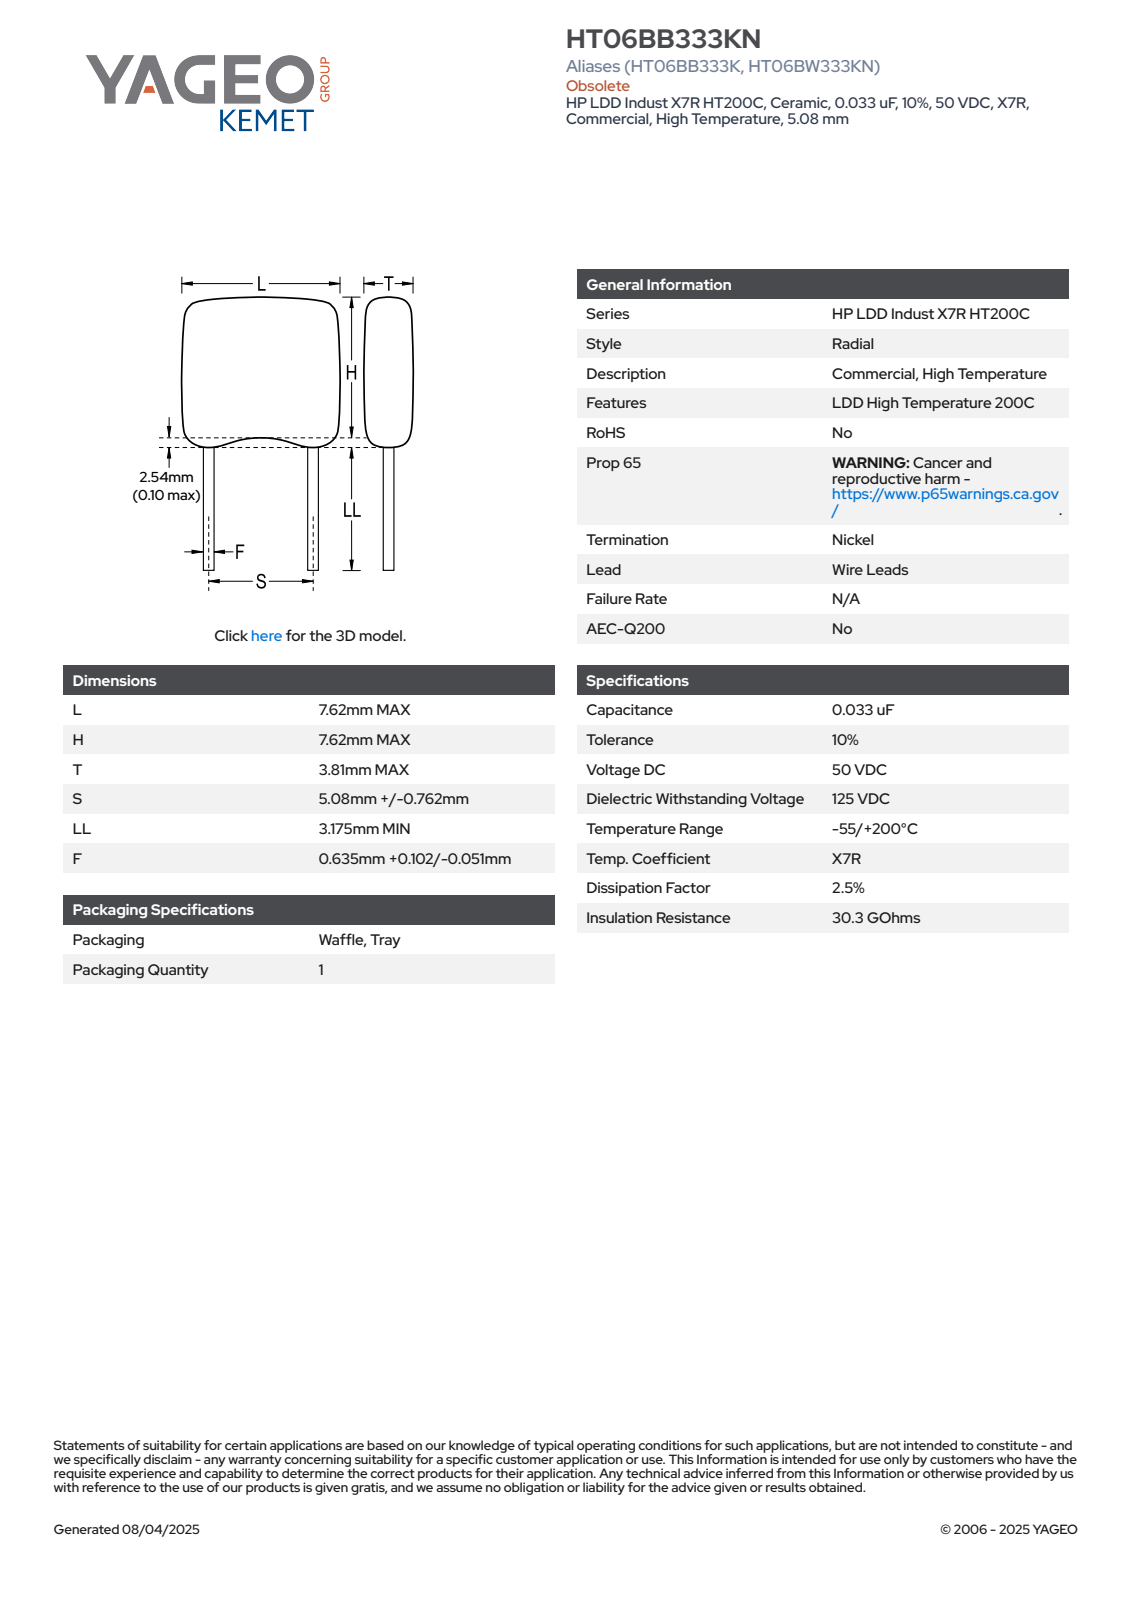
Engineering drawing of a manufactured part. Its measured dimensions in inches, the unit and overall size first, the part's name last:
Units: inches
Overall size (bounding box): 1.55 × 0.3 × 0.15
Round bosses / shafts (diameter × count): ⌀0.025 ×2
Main face-to-face distances: 0.15, 0.3, 1.25, 1.55, 1.425, 0.175, 0.125, 1.378, 0.128, 0.048
Volume: 0.015 in³ · Surface area: 0.57 in²
Bodies: 4 solids, 69 faces (65 planar, 4 cylindrical, 0 other)
Part name (STEP PRODUCT): CCR_RMST_HT06_L7.62H7.62T3.81S5.84LL31.75F0.635
STEP written by: SolidWorks 2014 (AUTOMOTIVE_DESIGN)
